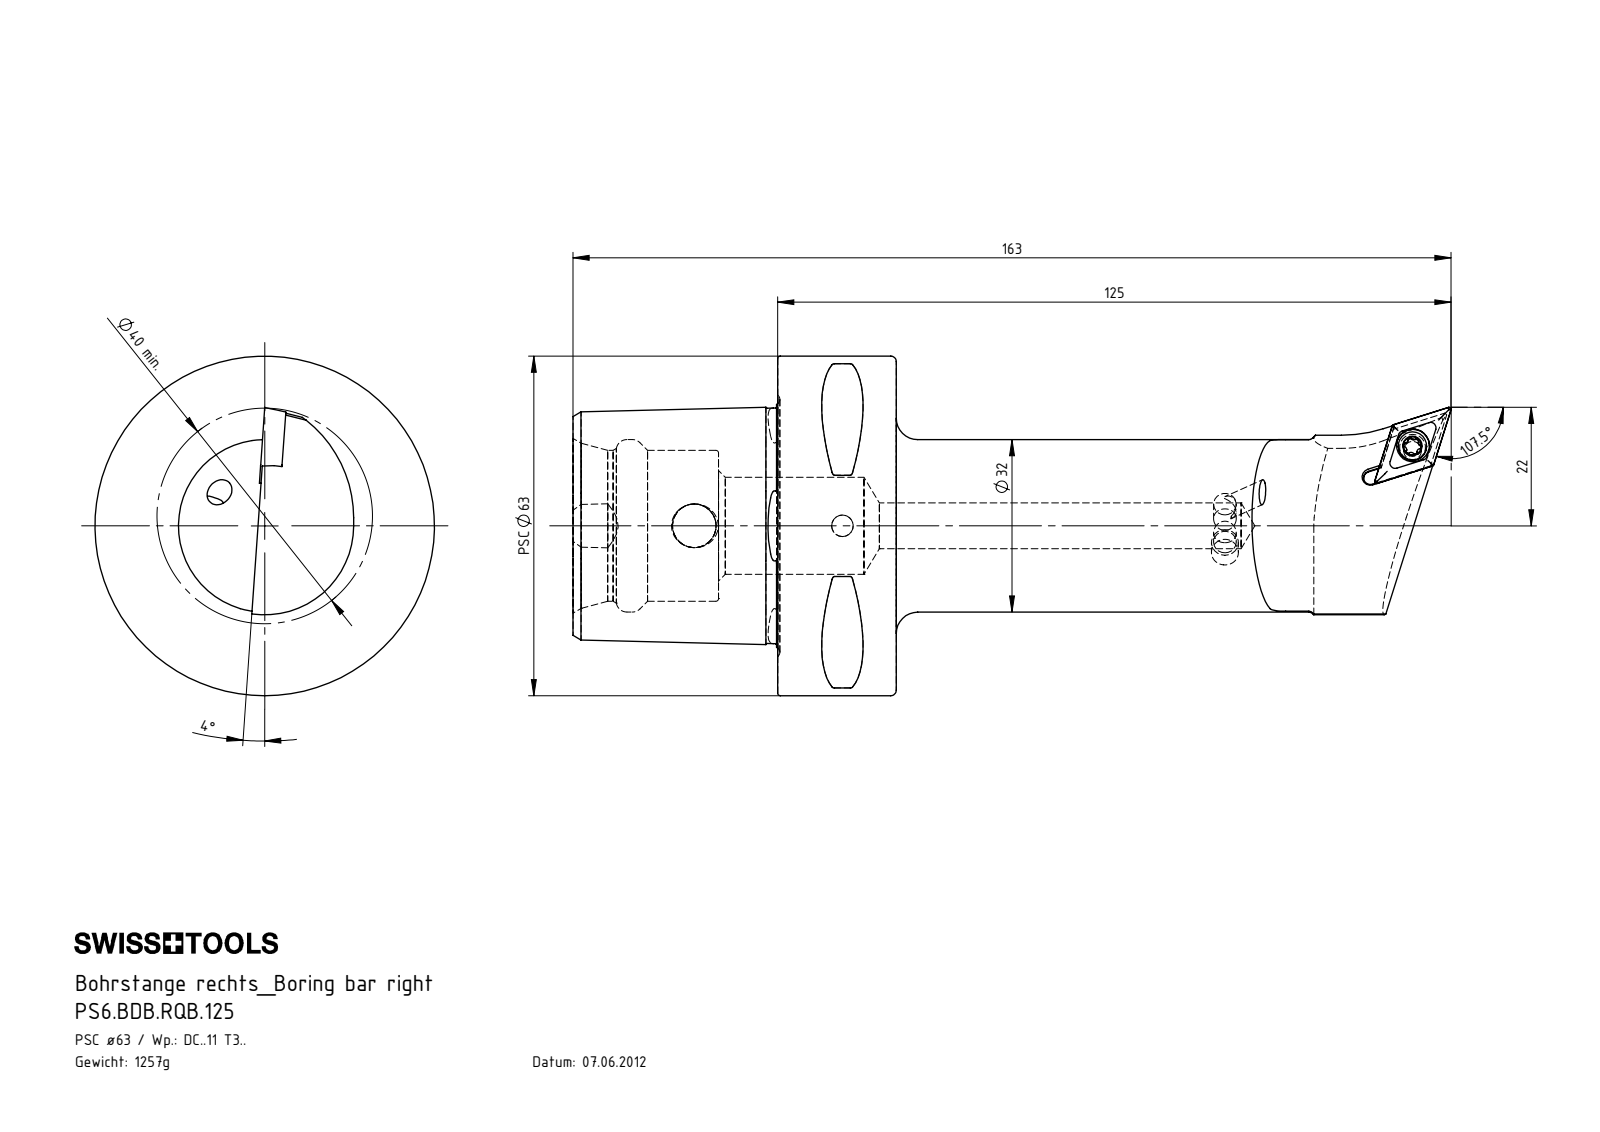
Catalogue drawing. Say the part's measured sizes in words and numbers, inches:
The part is named "DCMT11T304; KVT_MB_600_050; PS6-BDB.RQB.125_A; PS6.BDB.RQB.125 (+1 more)". Its 3-D file was written by "SolidWorks 2017 (AUTOMOTIVE_DESIGN)". It is 5 solids with 287 faces: 53 planar, 73 cylindrical and 161 other. Overall it measures 6.417 by 2.48 by 2.48 inches. Its volume is 9.818 cubic inches and its surface area 49.87 square inches. Round holes: 2 of diameter 0.157, 2 of diameter 0.165, 1 of diameter 0.13, 1 of diameter 0.173, 1 of diameter 0.24, 1 of diameter 0.319, 1 of diameter 0.335, 1 of diameter 0.709, 1 of diameter 1.102, 1 of diameter 1.26. Round bosses or shafts: 1 of diameter 2.48, 1 of diameter 0.207, 1 of diameter 0.197, 1 of diameter 0.157. Partial cylindrical surfaces (rounded edges, fillets, slot ends): 8 of radius 0.02, 6 of radius 0.013, 6 of radius 0.023, 1 of radius 0.049, 1 of radius 0.118, 1 of radius 0.236, 1 of radius 0.65, 1 of radius 0.906. The main face-to-face distances are 0.866, 1.496, 2.362, 0.98, 1.063, 0.433, 1.299, 2.197, 0.144, 1.488. The hole center spacings are 1.083.
